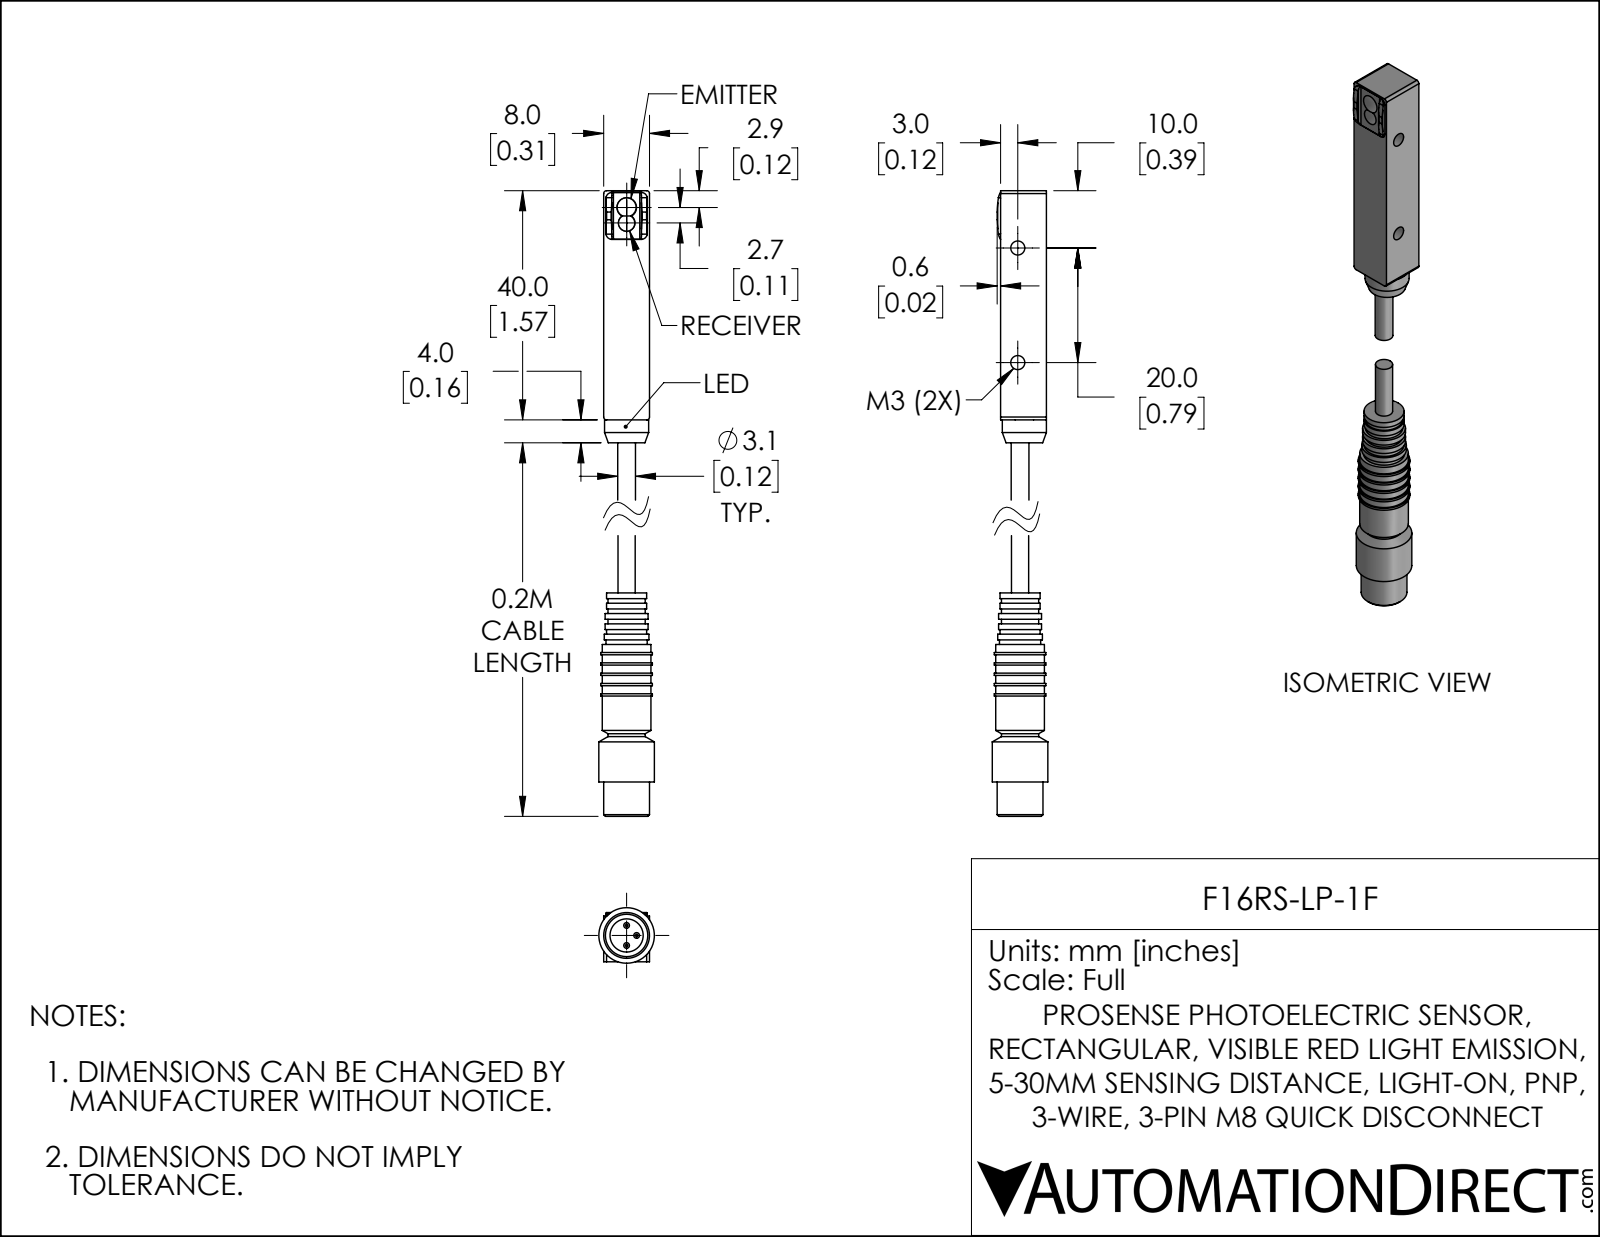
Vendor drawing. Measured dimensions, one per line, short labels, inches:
name: F16RS-LP-1F_1; F16RS-LP-1F_2; F16RS-LP-1F
written by: SolidWorks 2019 (AUTOMOTIVE_DESIGN)
unit: in
bodies: 2 solids, 125 faces (57 planar, 59 cylindrical, 9 other)
size: 4.515 × 0.382 × 0.382
volume: 0.294 in³; area: 5.041 in²
holes: 2× ⌀0.097, 1× ⌀0.228
bosses: 3× ⌀0.039, 1× ⌀0.382, 1× ⌀0.354, 1× ⌀0.335, 1× ⌀0.315, 1× ⌀0.307, 1× ⌀0.303, 1× ⌀0.295
rounds: 8× R0.039, 4× R0.004, 4× R0.02, 2× R0.012, 2× R0.083, 2× R0.725
face distances: 0.315, 0.071, 0.142, 0.039, 0.354, 1.732, 2.98, 2.586, 0.213, 1.248
hole spacings: 0.787
